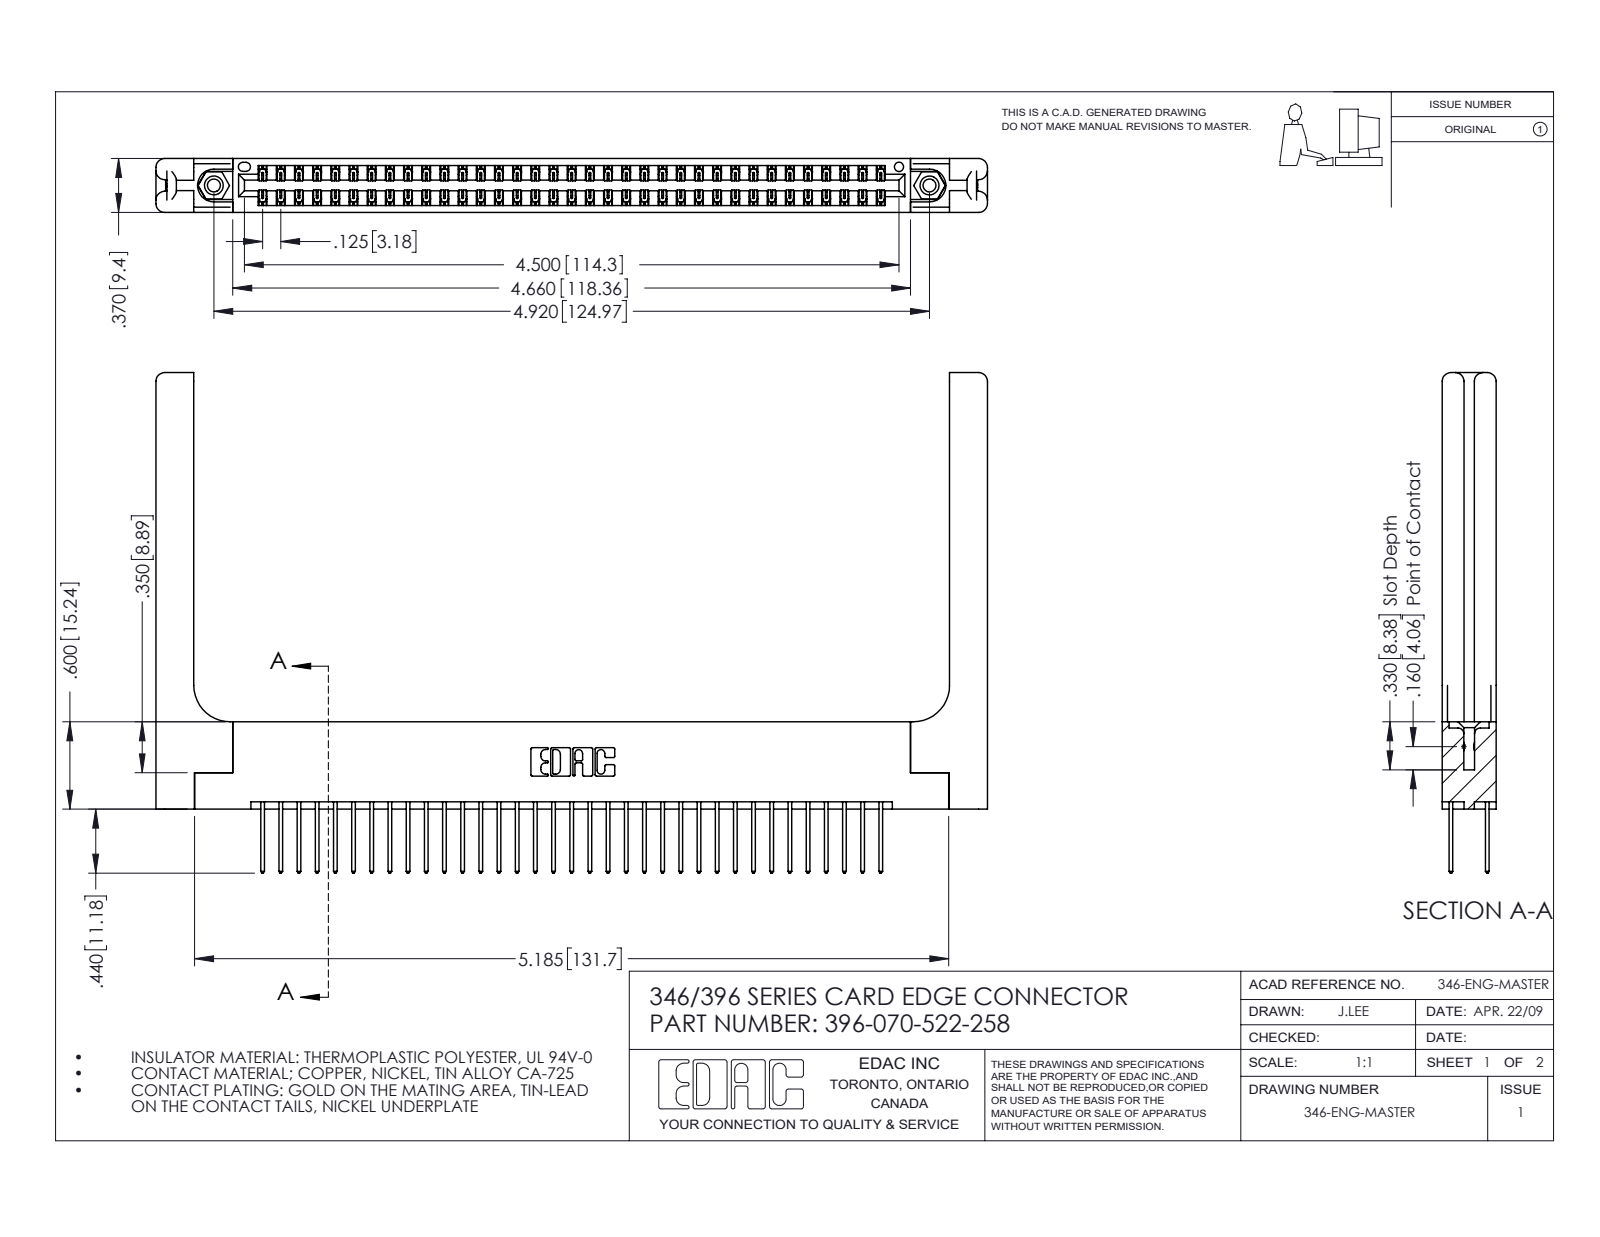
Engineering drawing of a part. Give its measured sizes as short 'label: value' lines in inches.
name: 345-250-001_345-250-001-102; 346 Part_Flush Mounting Lugs - 0.156 Dia-TH; 345-292-001_345-293-122; 346-220-058_345-220-058 (+1 more)
written by: SolidWorks 2016 (CONFIG_CONTROL_DESIGN)
unit: in
bodies: 75 solids, 4018 faces (2674 planar, 1284 cylindrical, 60 other)
size: 5.716 × 3.44 × 0.37
volume: 1.329 in³; area: 39.26 in²
holes: 2× ⌀0.089, 2× ⌀0.125, 2× ⌀0.156, 1× ⌀0.064
bosses: 2× ⌀0.155
rounds: 105× R0.006, 70× R0.01, 22× R0.01, 16× R0.06, 6× R0.007, 6× R0.031, 3× R0.026, 2× R0.014
face distances: 0.048, 0.322, 0.37, 0.072, 0.25, 0.025, 0.298, 0.148, 0.15, 0.275
hole spacings: 0.246, 4.711, 4.92
